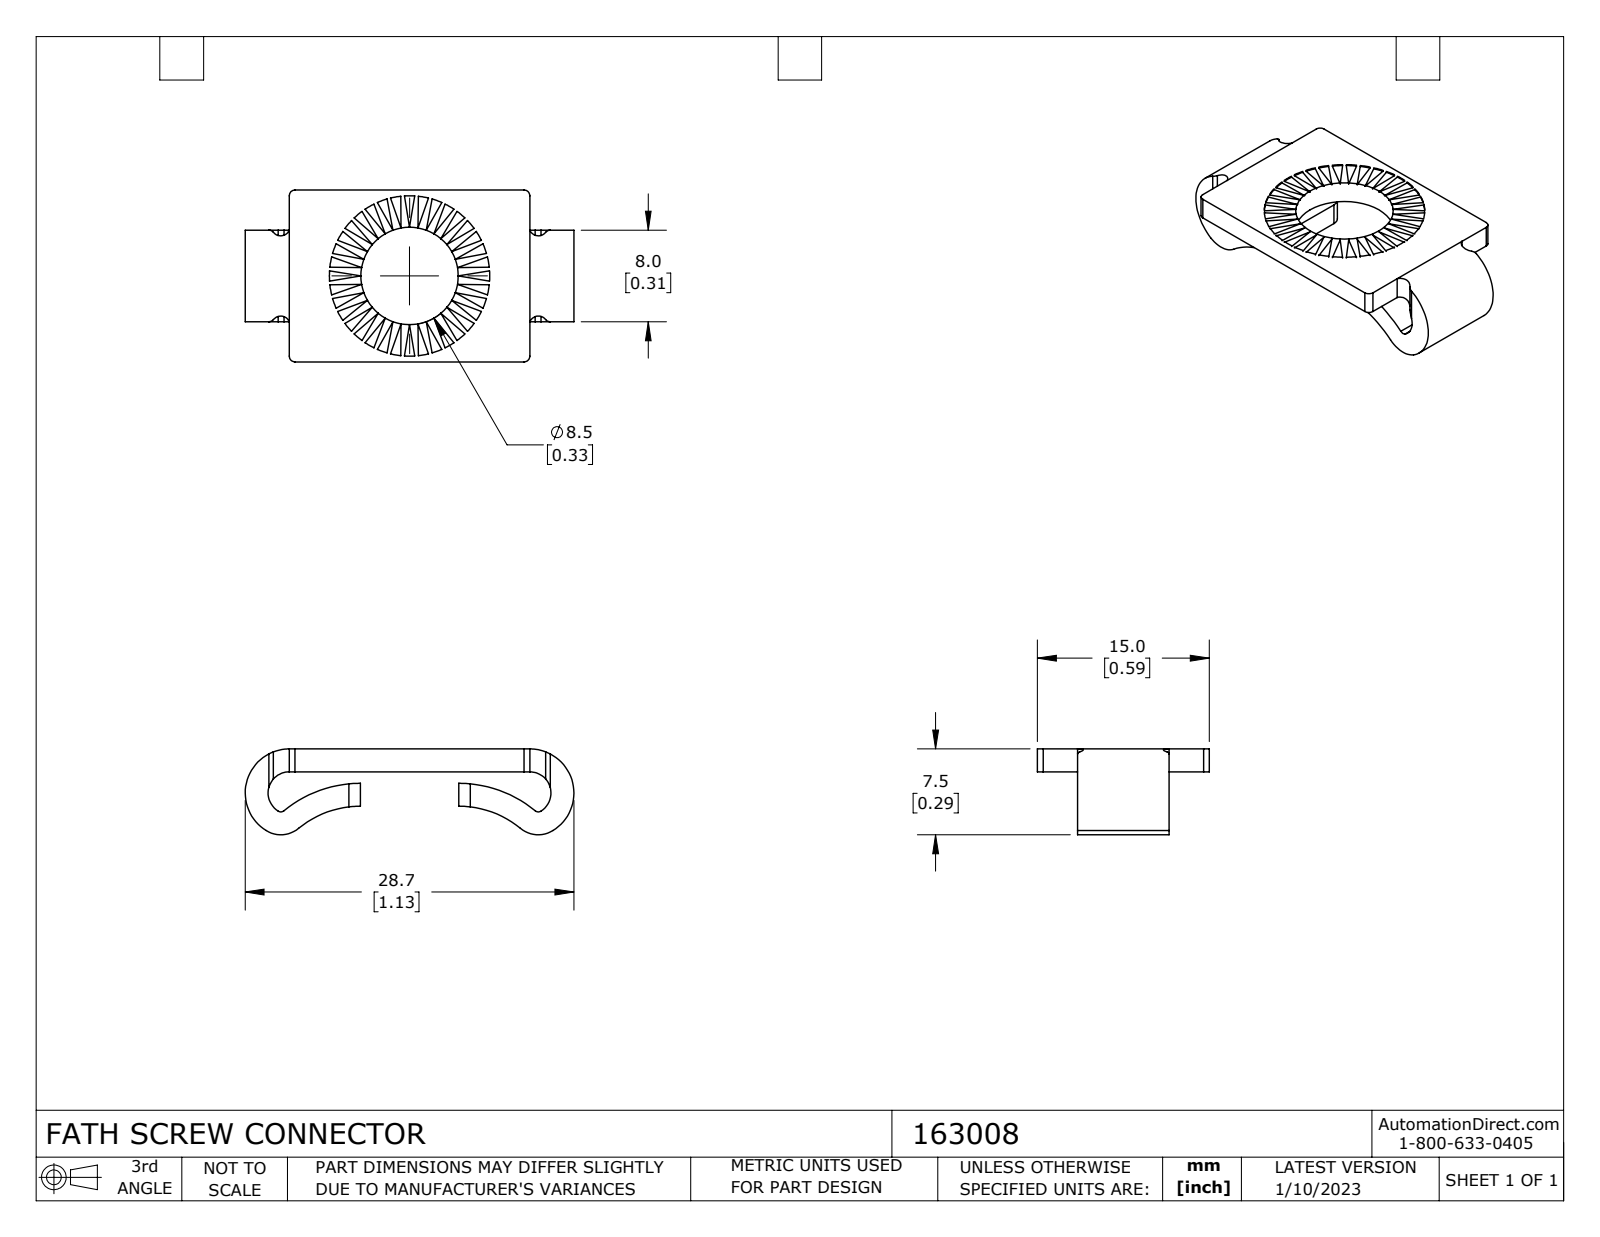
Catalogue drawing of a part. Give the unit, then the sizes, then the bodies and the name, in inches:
Units: inches
Overall size (bounding box): 1.13 × 0.591 × 0.295
Round holes (diameter × count): ⌀0.335 ×1
Partial cylindrical surfaces — rounded edges, fillets, slot ends (radius × count): R0.02 ×8, R0.032 ×4, R0.039 ×4, R0.017 ×2, R0.073 ×2, R0.096 ×2, R0.152 ×2, R0.333 ×2
Main face-to-face distances: 0.079, 0.138, 0.453, 0.315, 0.075, 0.591, 0.244, 0.583, 0.339, 0.827
Volume: 0.062 in³ · Surface area: 2.065 in²
Bodies: 1 solid, 117 faces (50 planar, 67 cylindrical, 0 other)
Part name (STEP PRODUCT): 163008
STEP written by: SolidWorks 2021 (CONFIG_CONTROL_DESIGN)
